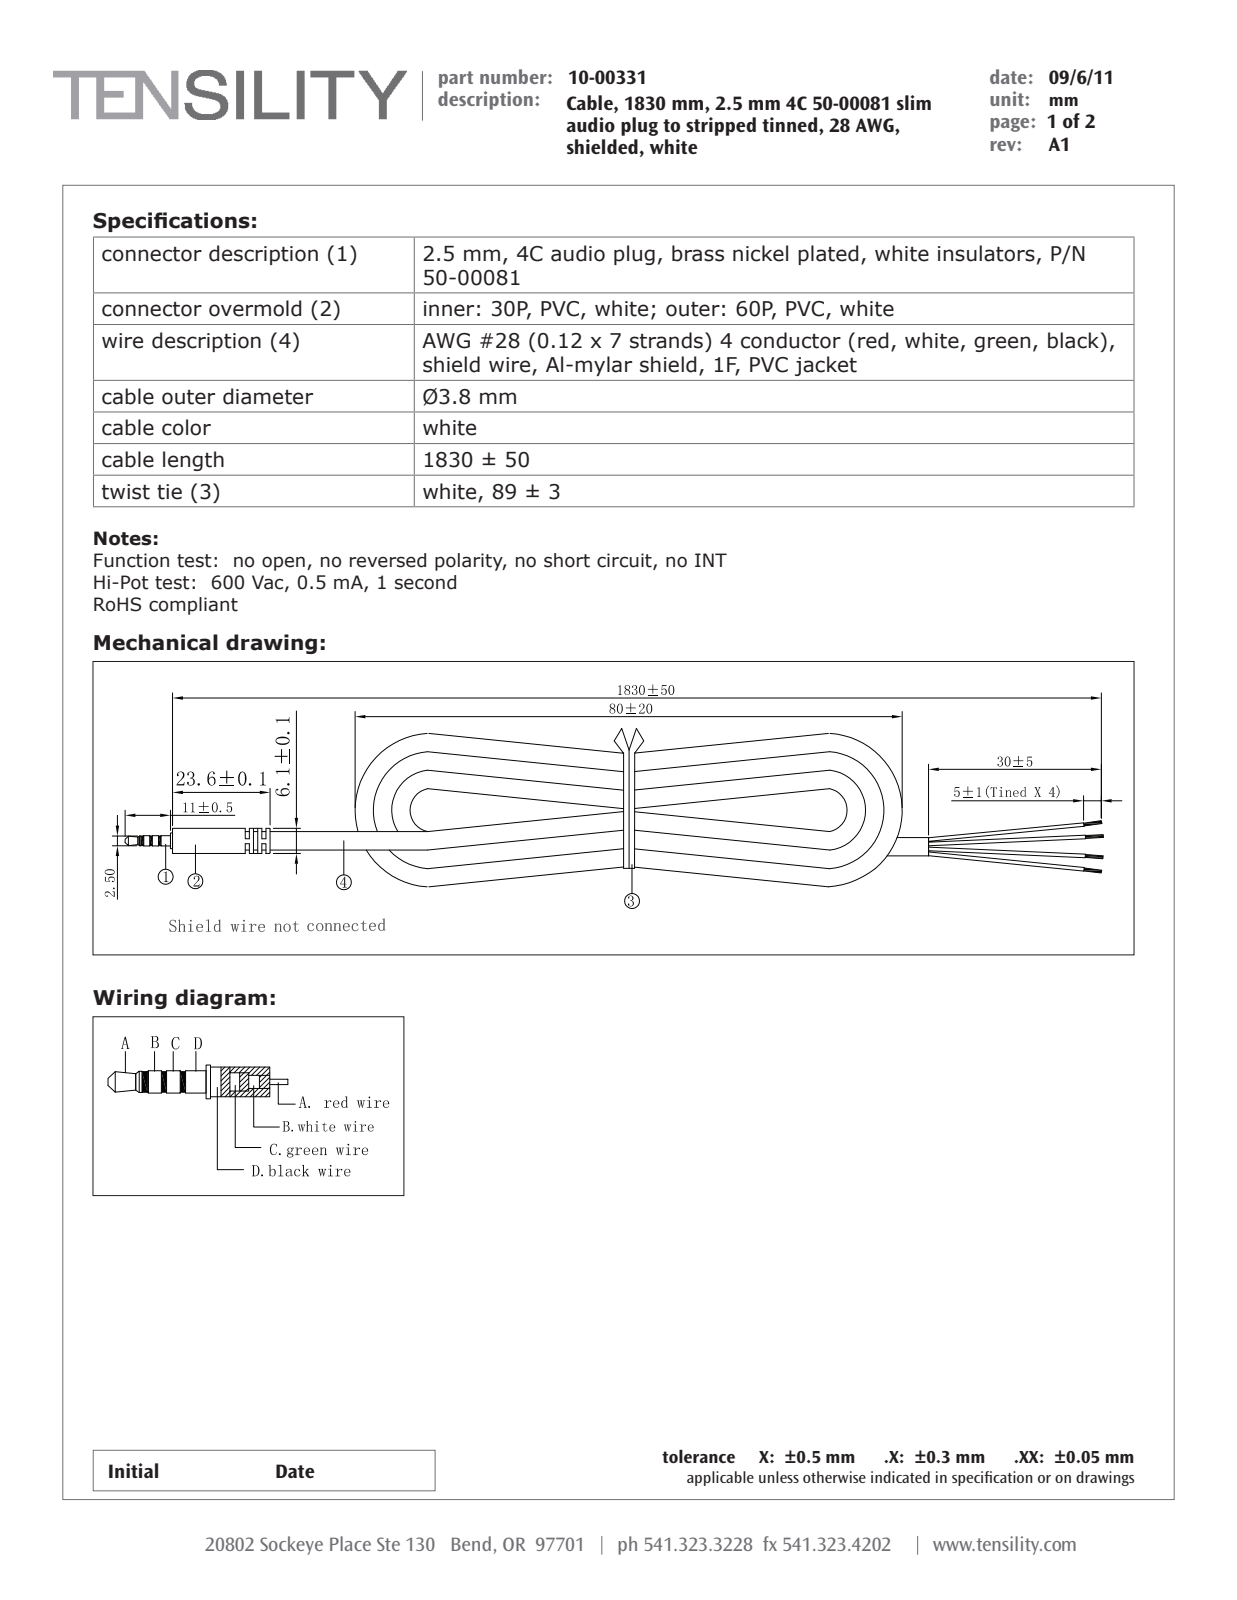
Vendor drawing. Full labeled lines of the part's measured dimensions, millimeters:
Part name (STEP PRODUCT): 24-00028; 30-00181_no heat shrink, no shield; 10-00331_revA4; 50-00407
STEP written by: SolidWorks 2015 (CONFIG_CONTROL_DESIGN)
Units: millimetres
Bodies: 124 solids, 818 faces (308 planar, 460 cylindrical, 50 other)
Overall size (bounding box): 209.4 × 6.85 × 6.1
Volume: 2 466 mm³ · Surface area: 20 066 mm²
Round holes (diameter × count): ⌀0.85 ×4, ⌀2.09 ×1, ⌀2.14 ×1
Round bosses / shafts (diameter × count): ⌀6.1 ×1, ⌀5.8 ×1, ⌀4.5 ×1, ⌀3.8 ×1, ⌀3 ×1, ⌀2.5 ×1, ⌀2.49 ×1, ⌀2.46 ×1
Partial cylindrical surfaces — rounded edges, fillets, slot ends (radius × count): R0.2 ×1, R0.8 ×1, R0.8 ×1, R1.5 ×1, R2 ×1
Main face-to-face distances: 0.9, 1.8, 2.7, 3.6, 4.5, 5.4, 17.9, 1.2, 23.3, 18.4
Hole centre spacings: 1.14, 0.39, 0.77, 0.52, 0.64, 0.89, 1.01, 1.73
